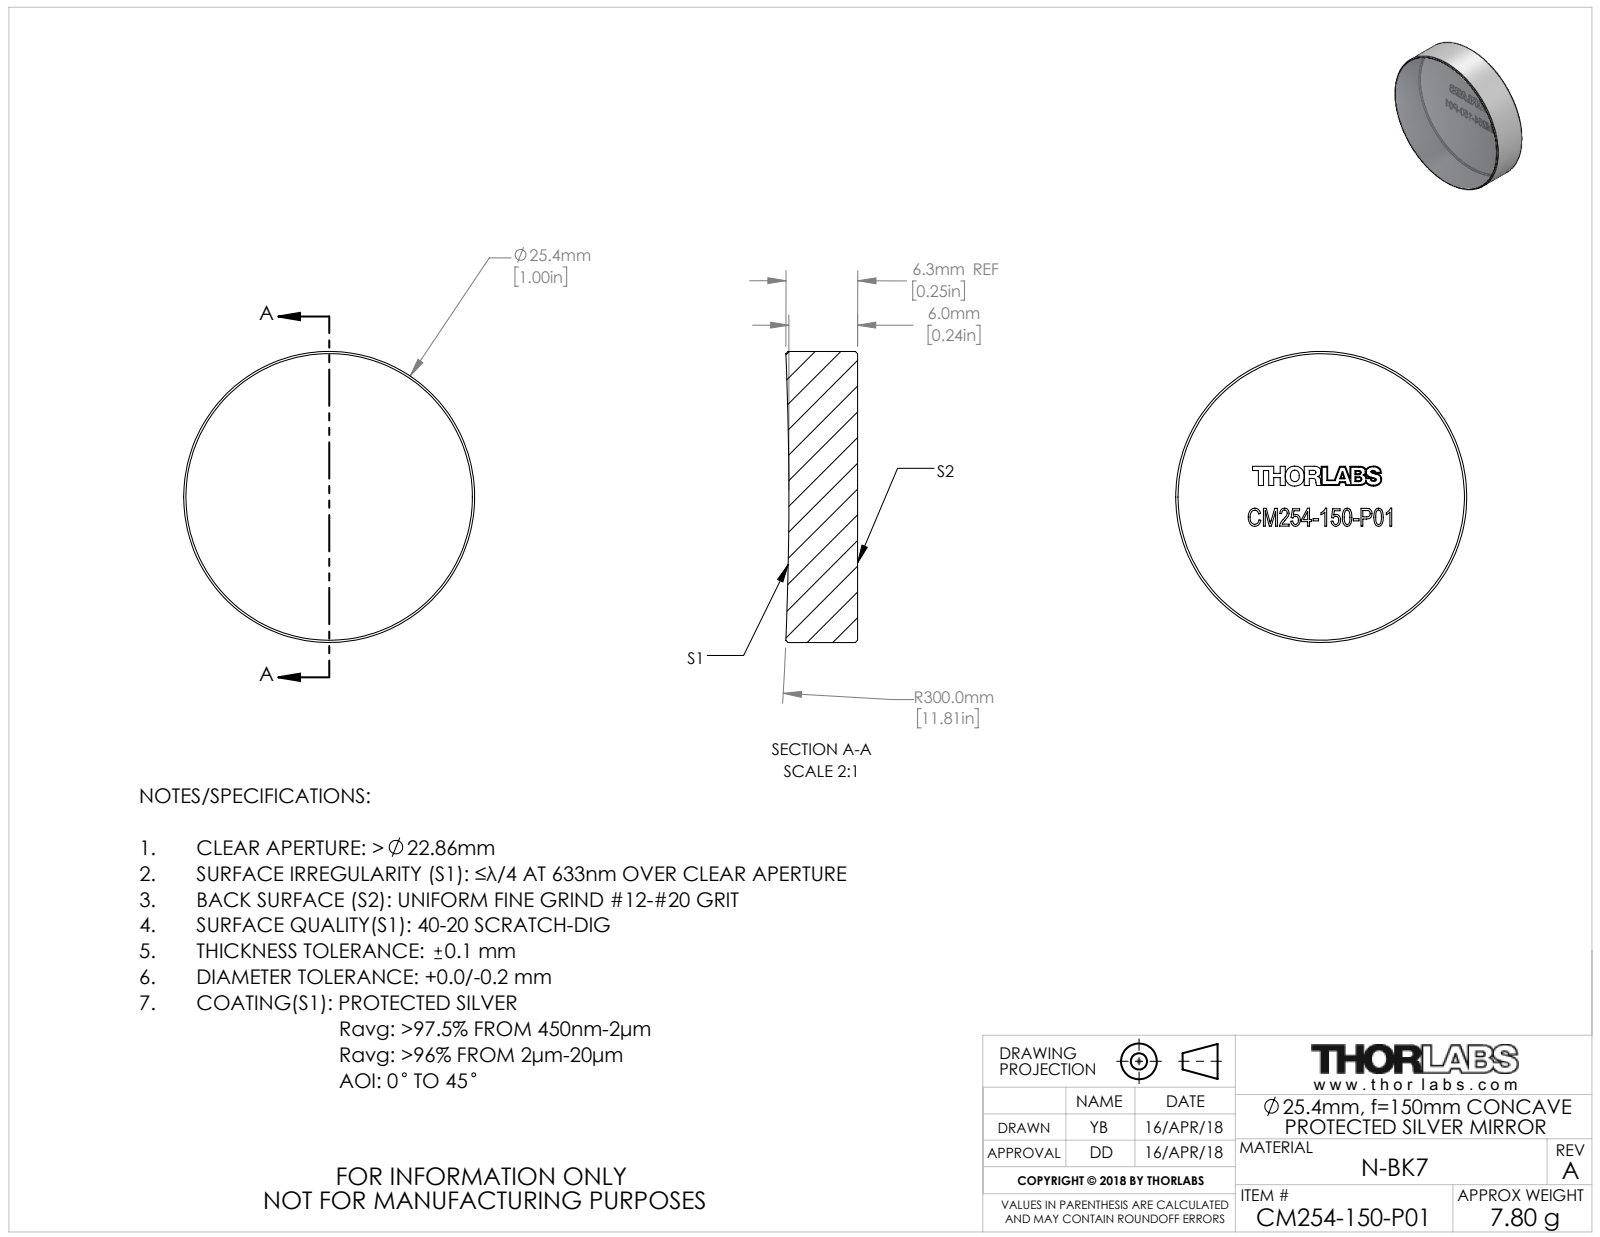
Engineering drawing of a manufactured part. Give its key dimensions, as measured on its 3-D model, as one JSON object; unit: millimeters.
{"part_name": "TTN153276-E0W", "step_written_by": "SolidWorks 2018 (CONFIG_CONTROL_DESIGN)", "units": "millimeters", "bodies": {"solids": 1, "faces": 41, "planar": 33, "cylindrical": 2, "other": 6}, "overall_size": [25.4, 25.4, 6.26], "volume_mm3": 3105, "surface_area_mm2": 1495, "round_bosses_or_shafts": [[25.4, 1]]}
